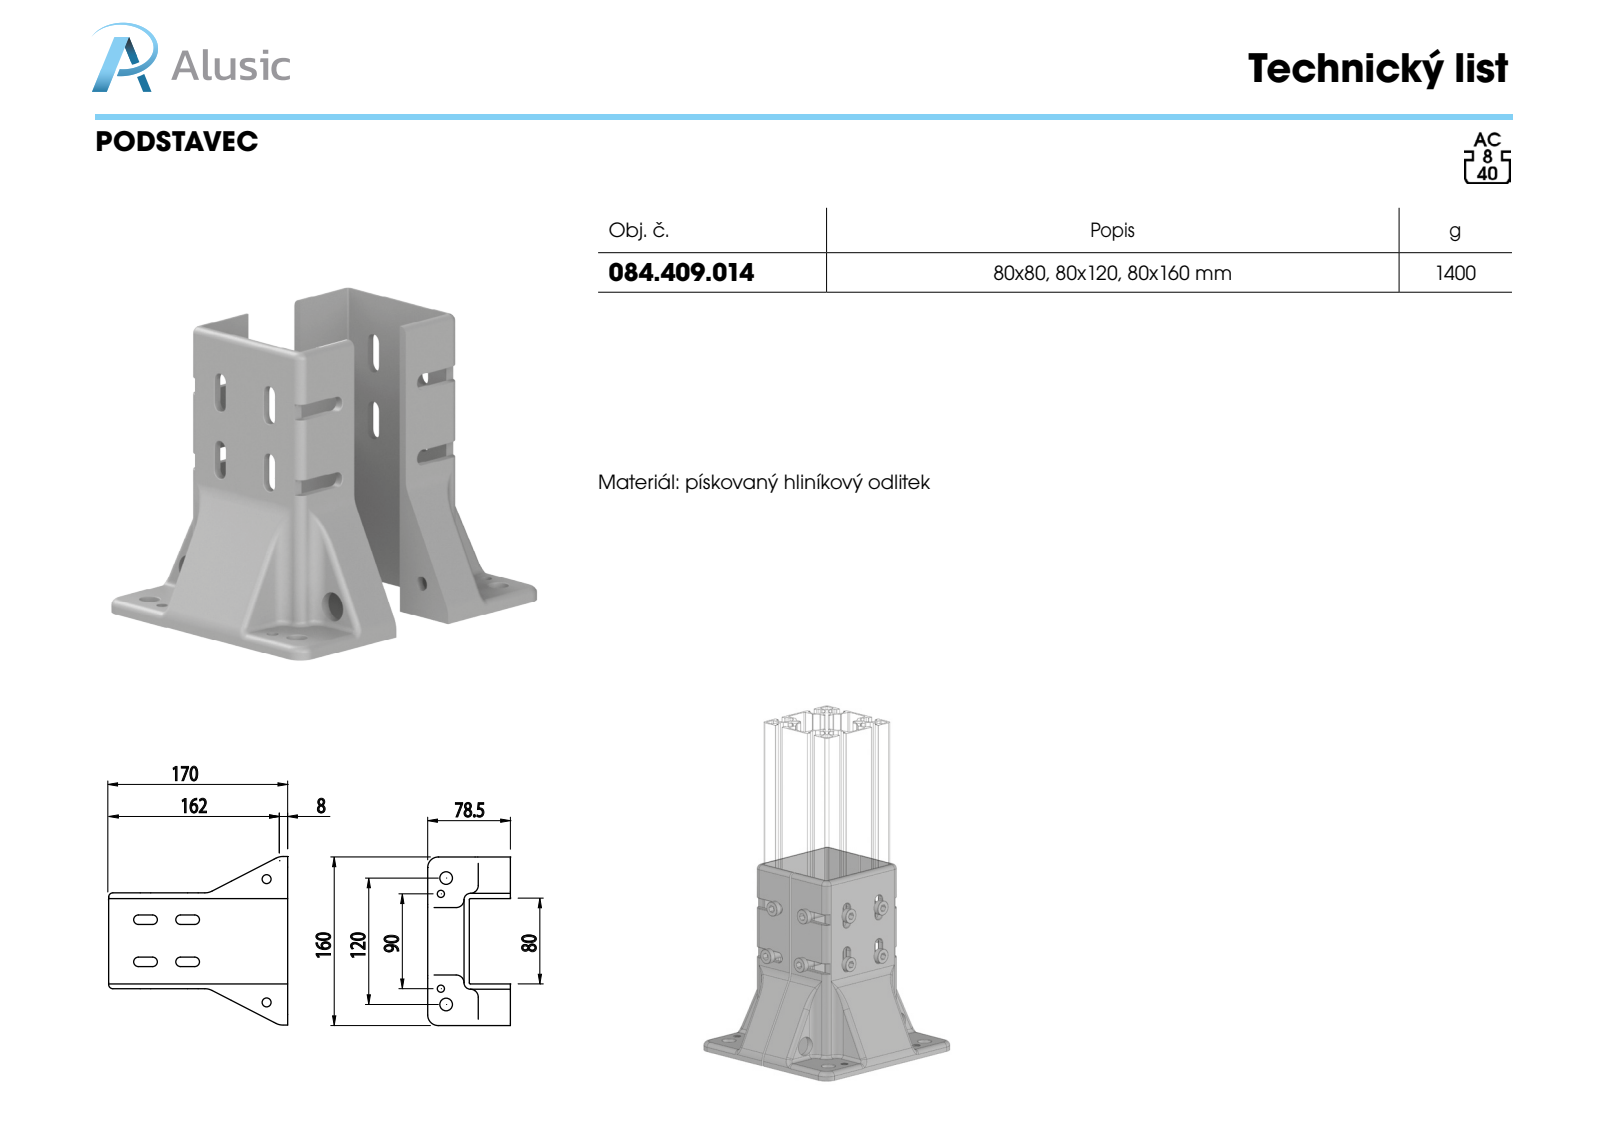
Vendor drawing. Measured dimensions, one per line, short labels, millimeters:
name: 084.409.014-L; 084.409.014
written by: SolidWorks 2016 (CONFIG_CONTROL_DESIGN)
unit: mm
bodies: 2 solids, 462 faces (114 planar, 206 cylindrical, 142 other)
size: 170 × 160 × 159
volume: 485 596 mm³; area: 187 025 mm²
holes: 4× ⌀6.8, 4× ⌀12, 2× ⌀8.5, 2× ⌀17
rounds: 40× R2, 16× R0.5, 16× R4, 12× R4.5, 8× R7.5, 4× R1, 4× R3, 4× R6
face distances: 5, 85, 86, 80, 81, 46, 39, 90, 44, 41
hole spacings: 15.81, 105.12, 129.87, 166.33, 90, 120, 124, 134
